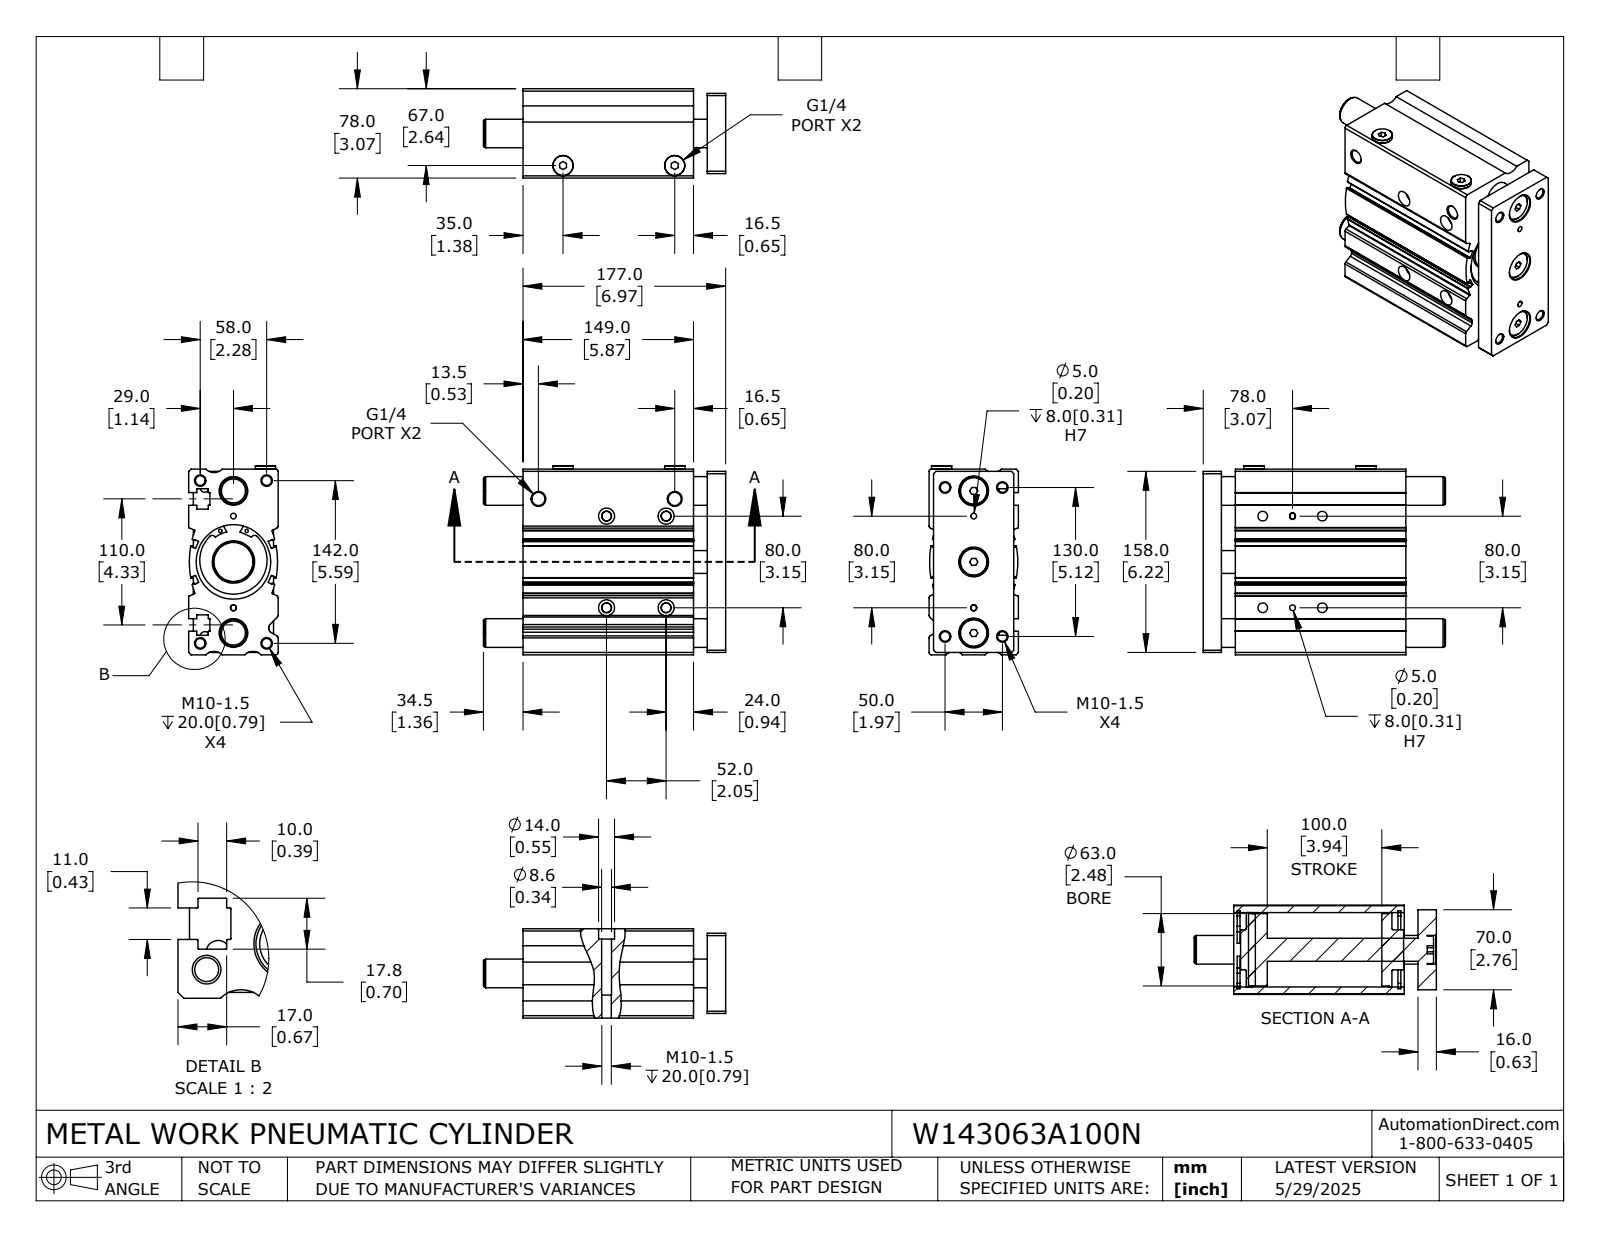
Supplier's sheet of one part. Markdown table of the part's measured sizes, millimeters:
| quantity | value |
| --- | --- |
| part name | W143063A100N; W143063A100N_ROD; W143063A100N_BODY |
| STEP written by | SolidWorks 2024 (CONFIG_CONTROL_DESIGN) |
| units | millimeters |
| bodies | 6 solids, 454 faces (182 planar, 216 cylindrical, 56 other) |
| overall size | 211.5 × 165 × 78 |
| volume | 1 572 000 mm³ |
| surface area | 283 700 mm² |
| round holes (diameter × count) | 8.4 × 12, 3 × 4, 5 × 4, 8.6 × 4, 14 × 4, 25 × 3, 11.4 × 2, 65 × 1 |
| round bosses / shafts (diameter × count) | 24 × 3, 17.7 × 2, 68 × 1, 64.8 × 1, 63 × 1, 35 × 1, 20 × 1 |
| partial cylindrical surfaces (radius × count) | 0.3 × 44, 0.5 × 12, 2 × 8, 2.5 × 4, 3 × 4, 10 × 3, 3.1 × 2, 29.4 × 2 |
| main face-to-face distances | 78, 16, 12, 28, 149, 177, 161, 162, 4, 18.5 |
| hole center spacings | 7.2, 17.3, 25.2, 26, 29.4, 30.4, 35.4, 36.8 |
